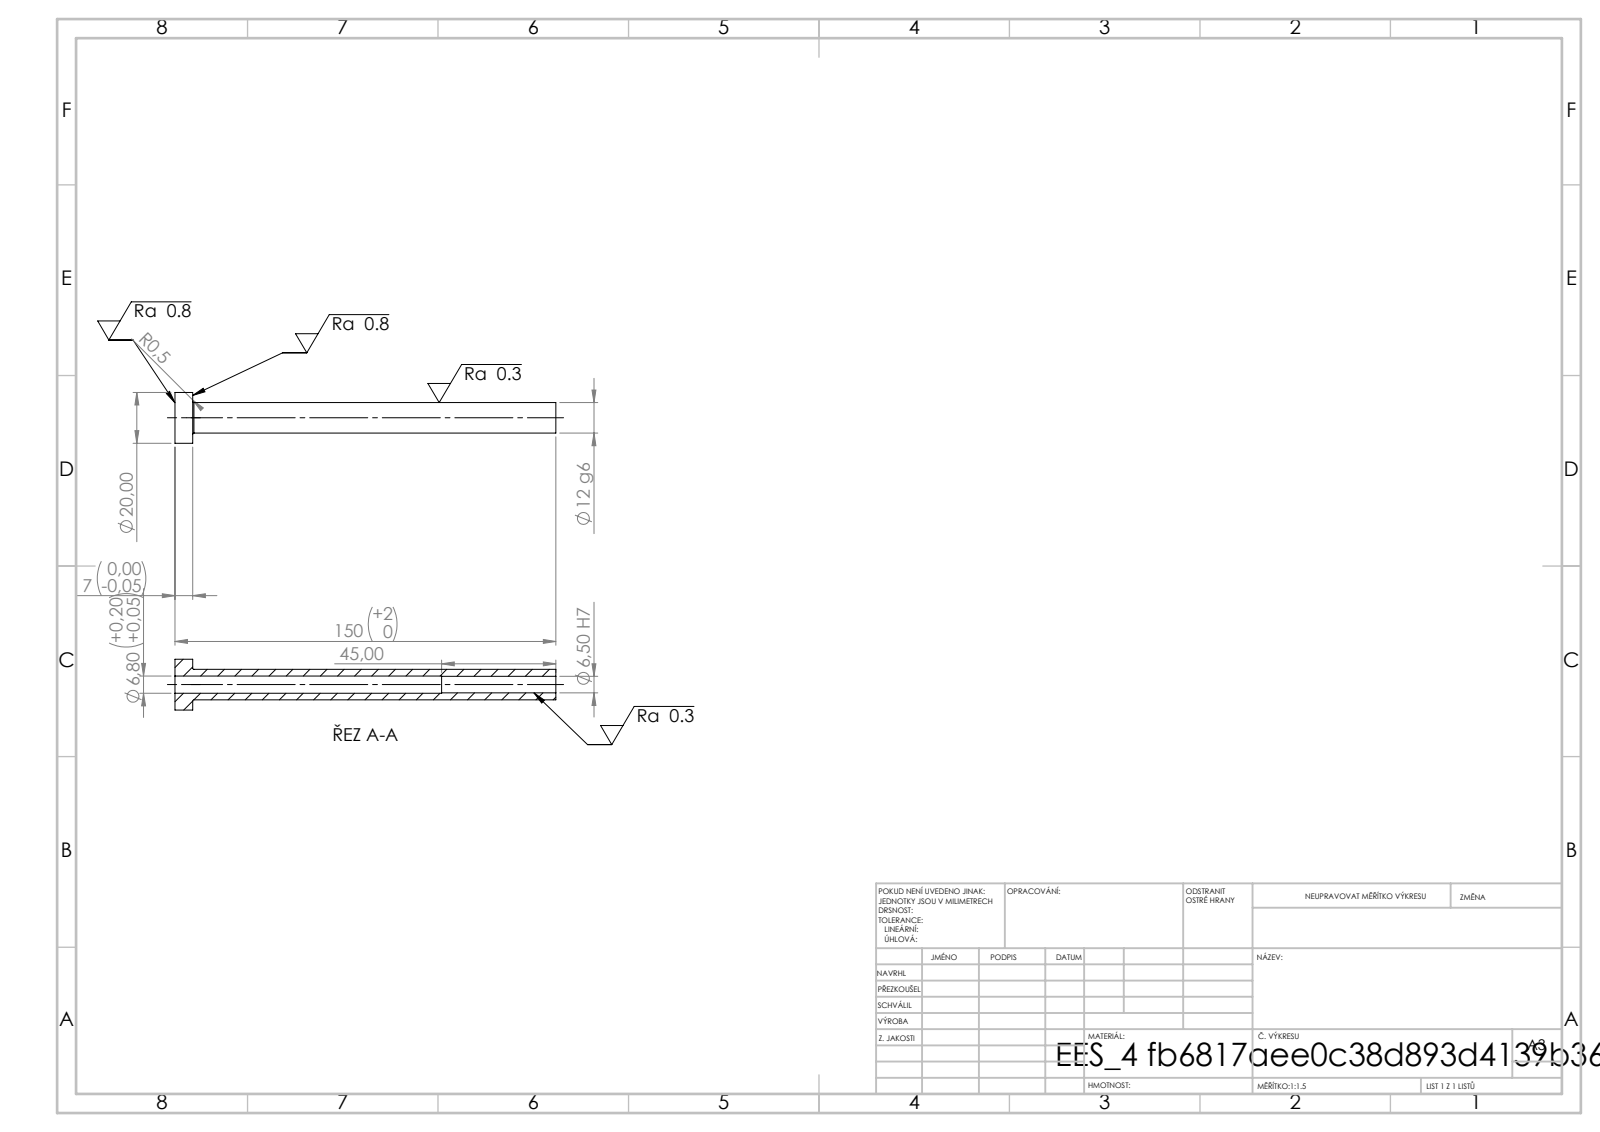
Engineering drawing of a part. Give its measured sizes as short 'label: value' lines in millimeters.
written by: SolidWorks 2019 (CONFIG_CONTROL_DESIGN)
unit: mm
bodies: 1 solid, 14 faces (4 planar, 8 cylindrical, 2 other)
size: 150 × 20 × 20
volume: 13 068 mm³; area: 9 547 mm²
holes: 1× ⌀6.5, 1× ⌀6.8
bosses: 1× ⌀20, 1× ⌀12
face distances: 7, 150, 143, 105, 98, 45
